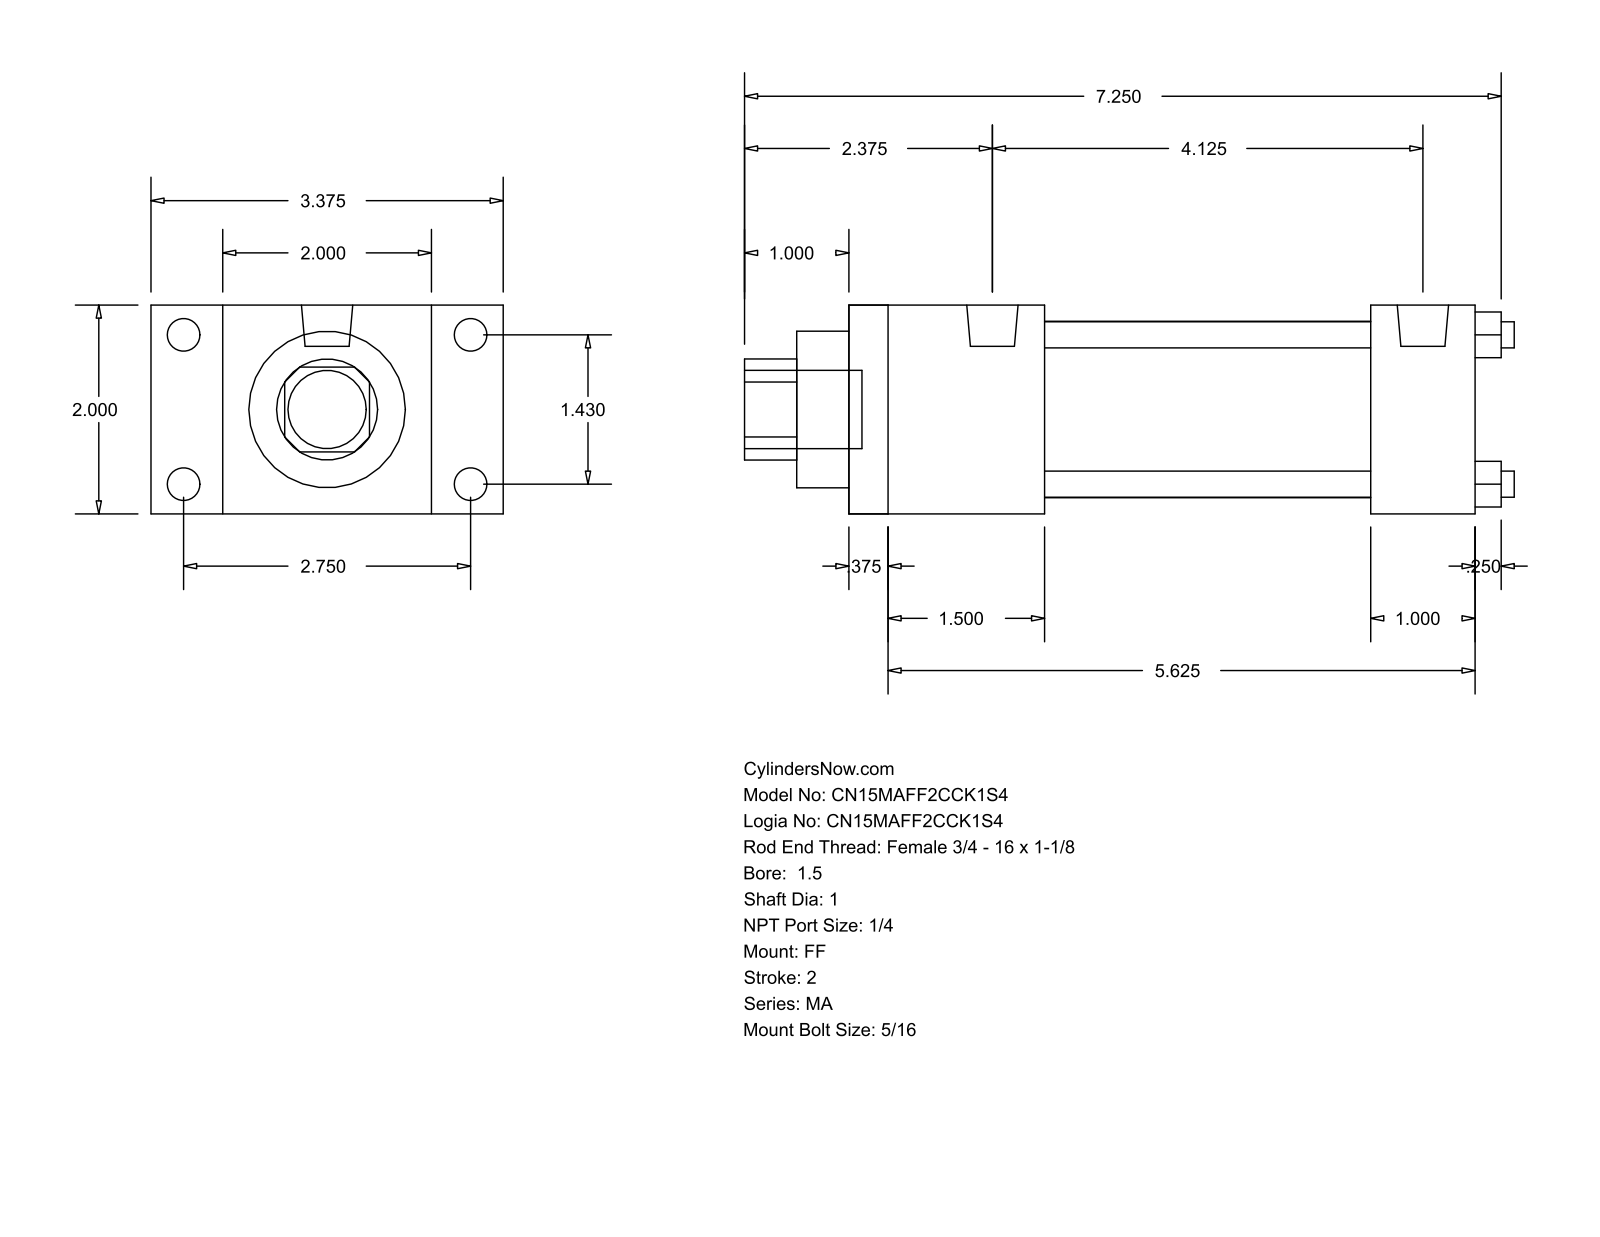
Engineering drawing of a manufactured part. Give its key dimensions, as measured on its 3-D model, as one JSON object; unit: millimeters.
{"part_name": "MA_FF__0150_1", "step_written_by": "GSSL Pune (CONFIG_CONTROL_DESIGN)", "units": "millimeters", "bodies": {"solids": 0, "faces": 92, "planar": 64, "cylindrical": 28, "other": 0}, "overall_size": [187.32, 85.72, 50.8], "round_holes": [[6.35, 4], [25.4, 1], [38.1, 1], [42.93, 1]], "round_bosses_or_shafts": [[7.94, 8], [12.49, 2], [19.05, 1]], "partial_cylinders_radius": [[12.29, 1]], "face_to_face_distances": [50.8, 152.4, 9.52, 142.88, 25.4, 47.63, 127, 38.11, 117.48, 79.37], "hole_center_spacings": [25.68, 36.32, 51.36]}
